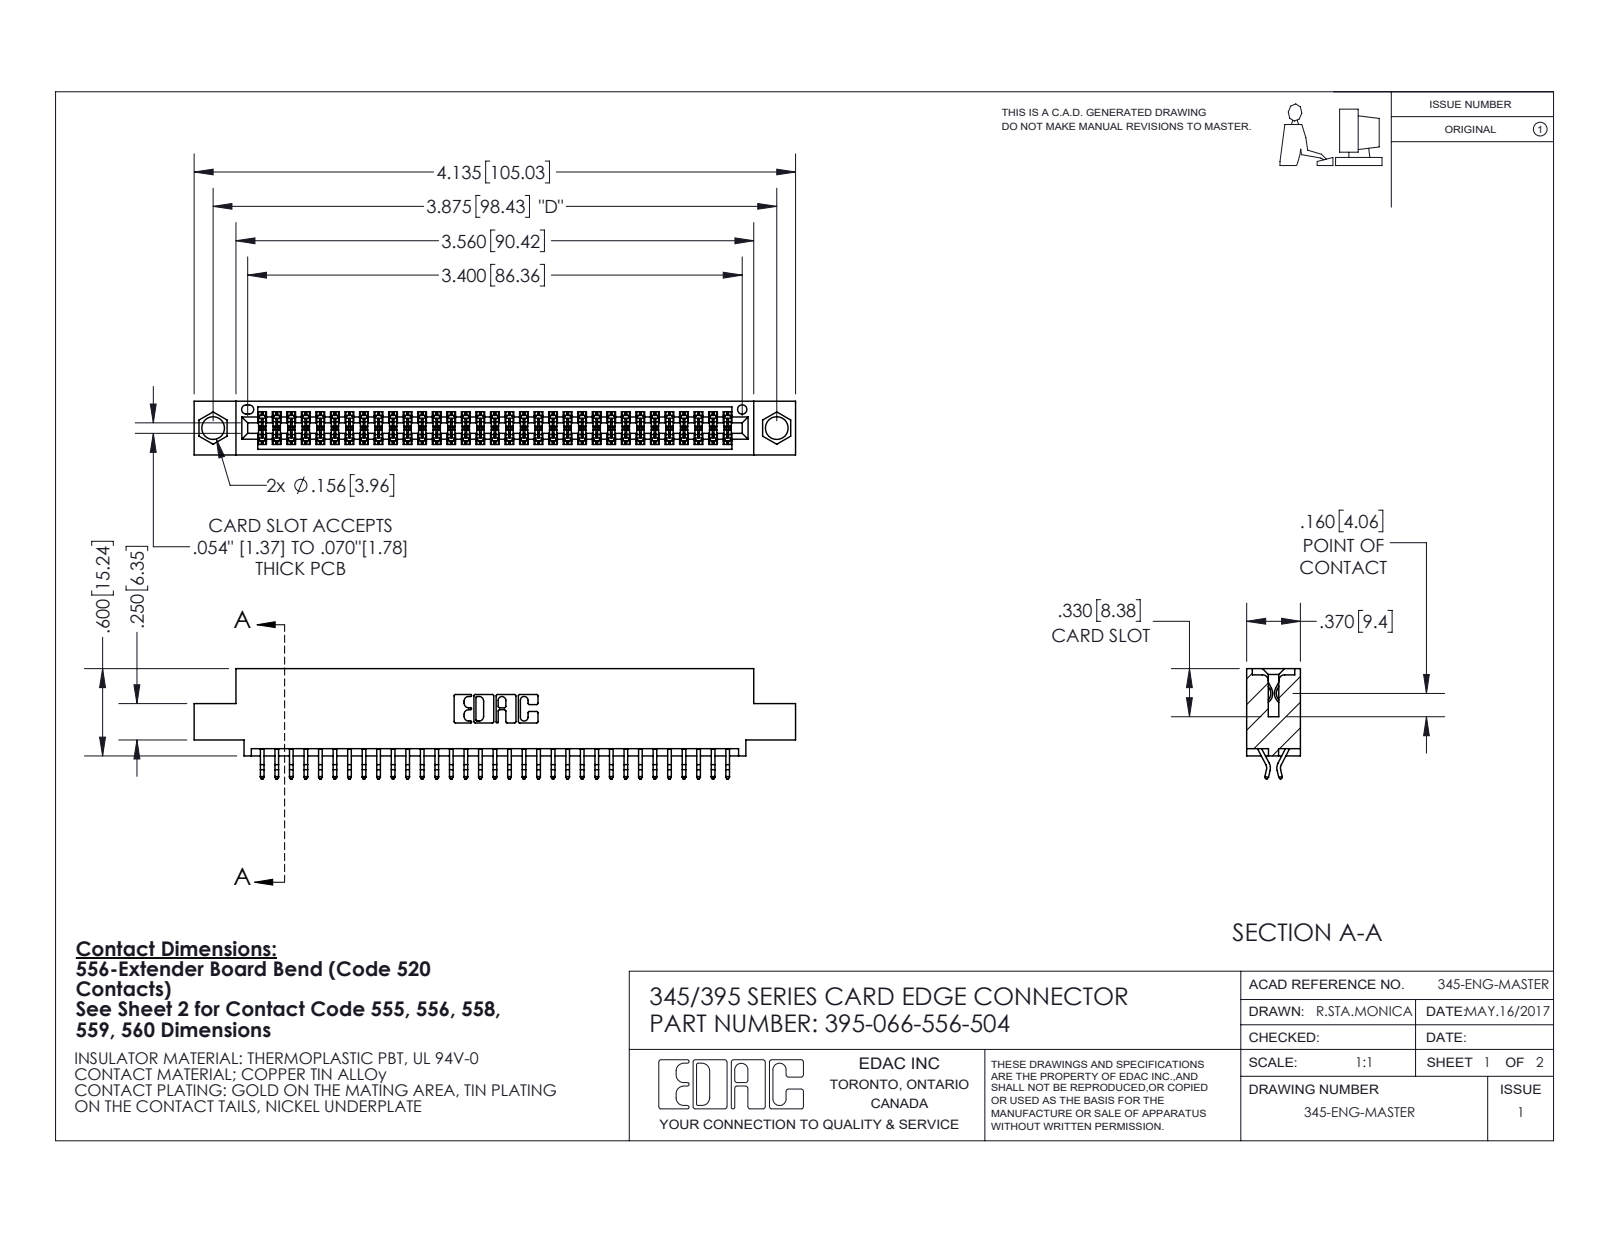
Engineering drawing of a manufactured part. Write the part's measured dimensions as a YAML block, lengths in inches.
part_name: "345 Part_0.110 Offset - 0.156 Dia-TI; 345-292-001_556 Tail; 395-066-556-504"
step_written_by: "SolidWorks 2020 (CONFIG_CONTROL_DESIGN)"
units: inches
bodies: {solids: 67, faces: 3840, planar: 2540, cylindrical: 1300, other: 0}
overall_size: [4.135, 0.757, 0.37]
volume: 0.606
surface_area: 22.32
round_holes:
  - {diameter: 0.156, count: 2}
  - {diameter: 0.064, count: 1}
partial_cylinders:
  - {radius: 0.006, count: 99}
  - {radius: 0.01, count: 22}
  - {radius: 0.007, count: 6}
  - {radius: 0.031, count: 6}
  - {radius: 0.026, count: 3}
  - {radius: 0.01, count: 2}
  - {radius: 0.014, count: 2}
  - {radius: 0.019, count: 2}
face_to_face_distances: [0.298, 0.072, 0.37, 0.2, 0.025, 0.098, 0.272, 0.225, 0.175, 0.149]
hole_center_spacings: [0.27, 3.64, 3.875]
